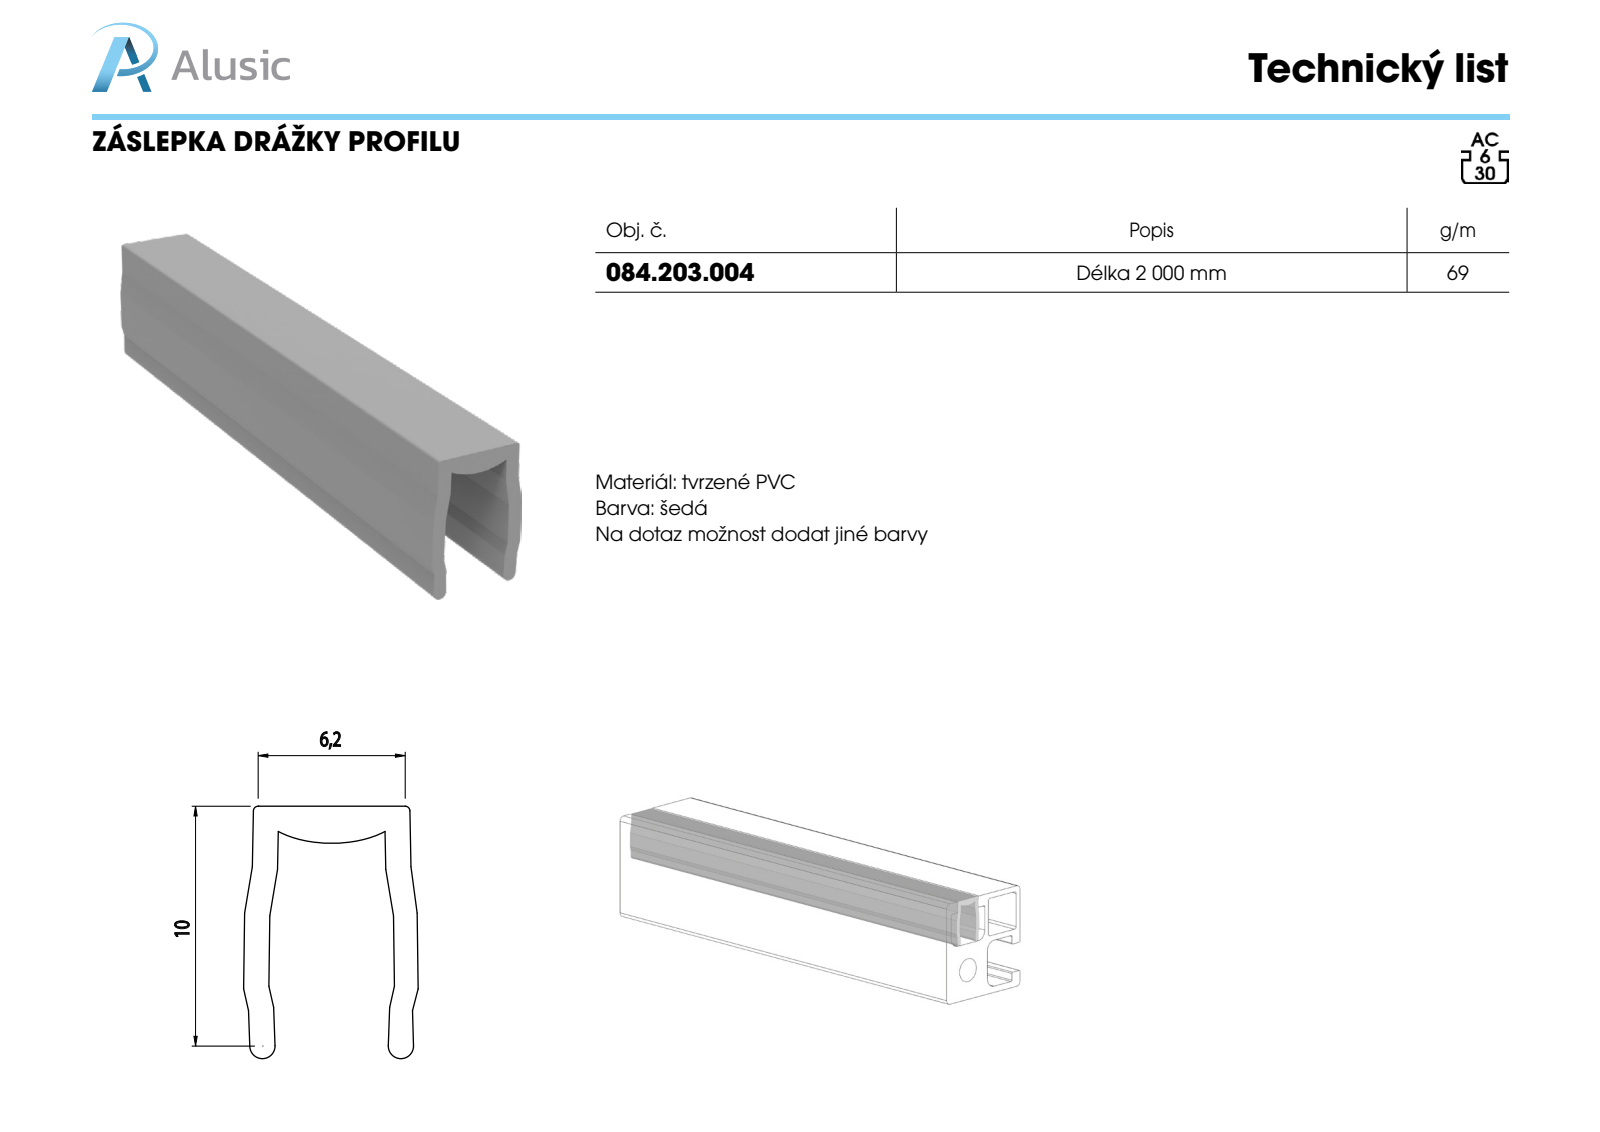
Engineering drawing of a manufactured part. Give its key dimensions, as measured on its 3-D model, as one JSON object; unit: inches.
{"part_name": "084.203.004", "step_written_by": "SolidWorks 2011 (CONFIG_CONTROL_DESIGN)", "units": "inches", "bodies": {"solids": 1, "faces": 28, "planar": 23, "cylindrical": 5, "other": 0}, "overall_size": [3.937, 0.394, 0.272], "volume_in3": 0.153, "surface_area_in2": 7.79, "partial_cylinders_radius": [[0.007, 2], [0.02, 2], [0.197, 1]], "face_to_face_distances": [0.039, 0.037, 3.937]}
